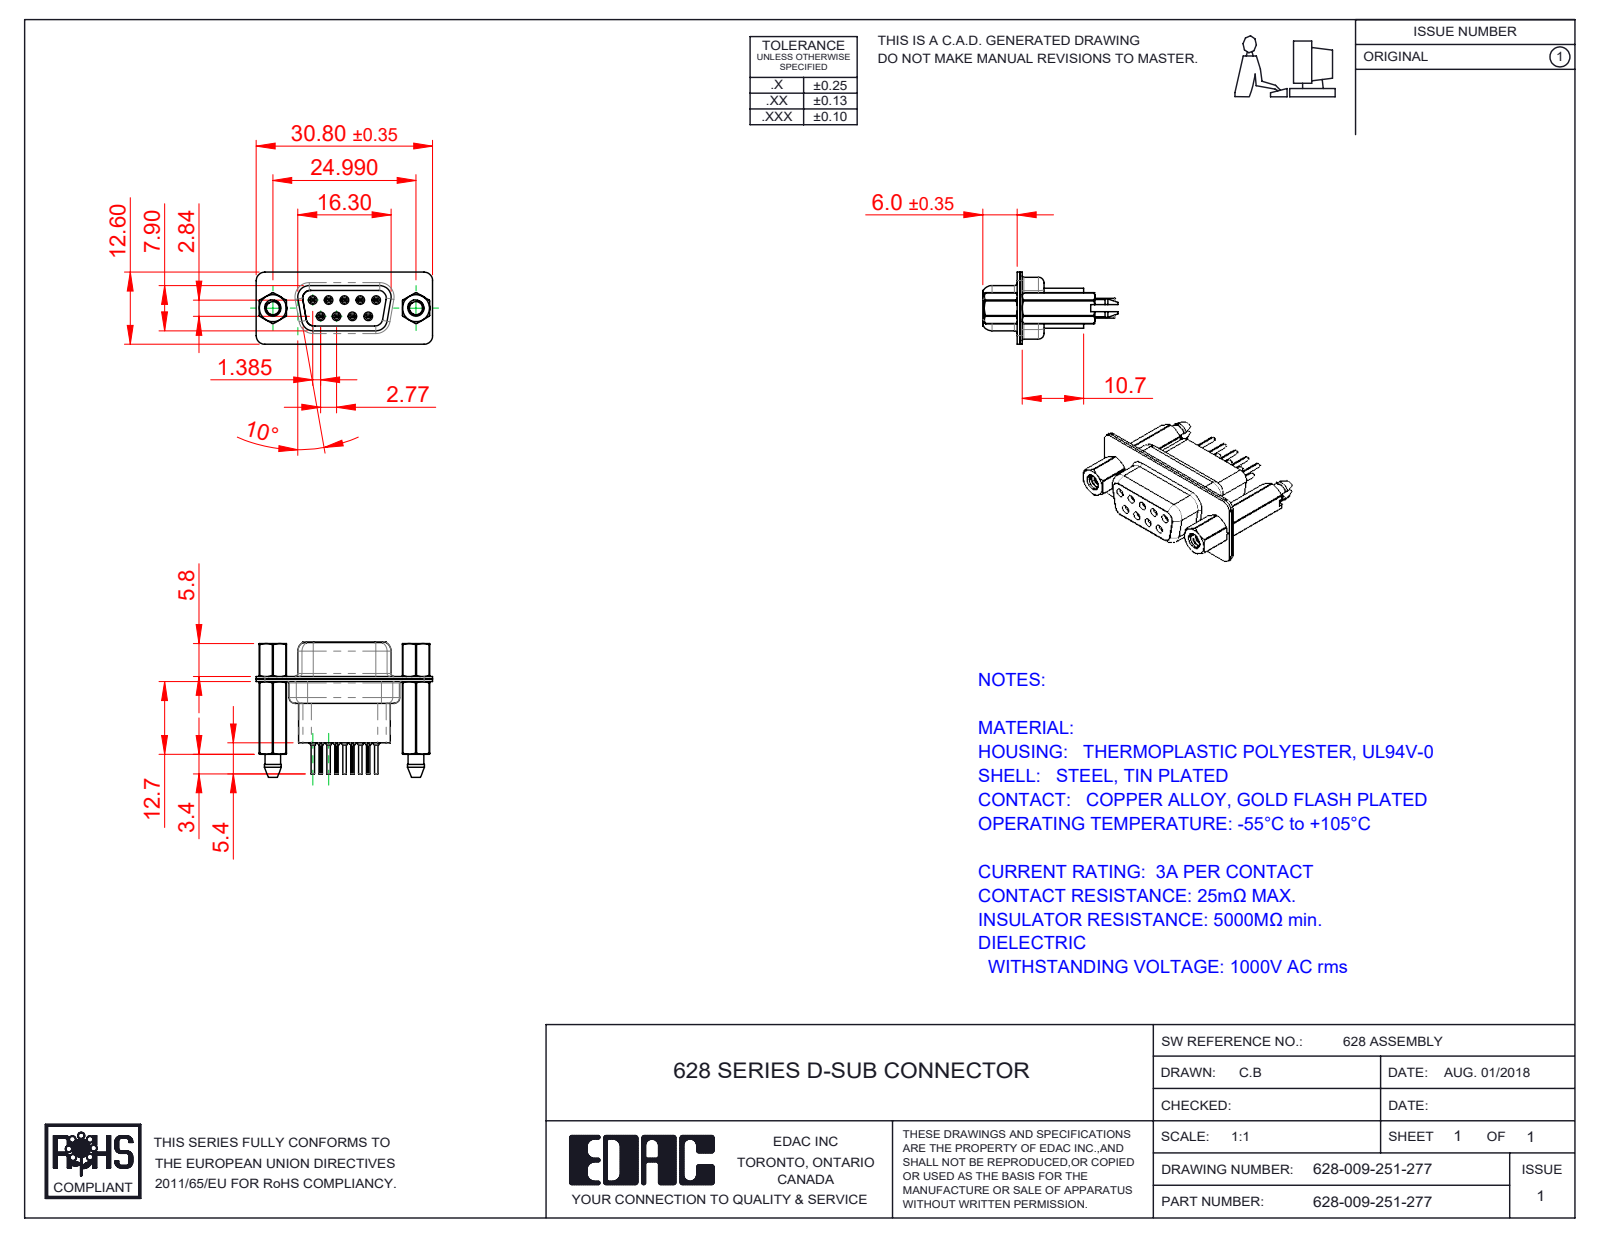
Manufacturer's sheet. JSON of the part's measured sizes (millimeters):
{"part_name": "628 Contact Row 2_51; 628 Shell Front_09 Contacts; 628 4-40 Hex Standoff; 628-009-251-277 (+4 more)", "step_written_by": "SolidWorks 2020 (CONFIG_CONTROL_DESIGN)", "units": "millimeters", "bodies": {"solids": 16, "faces": 1586, "planar": 400, "cylindrical": 538, "other": 648}, "overall_size": [30.8, 23.6, 12.6], "volume_mm3": 2771, "surface_area_mm2": 6452, "round_holes": [[0.2, 9], [0.8, 9], [0.9, 9], [1.1, 9], [1.6, 9], [1.7, 5], [2.26, 2], [2.29, 2], [4, 2], [4.05, 2], [4.85, 2]], "round_bosses_or_shafts": [[2, 9], [1.5, 9], [1.2, 9], [0.6, 9], [4.95, 2], [4.8, 2], [2.79, 2]], "partial_cylinders_radius": [[1.5, 19], [0.1, 18], [2, 12], [0.28, 9], [1.35, 6], [1.6, 6], [0.25, 4], [0.5, 4]], "face_to_face_distances": [0.45, 0.4, 0.9, 4.76, 8.5, 6.6, 1.9, 1.4, 7, 0.5], "hole_center_spacings": [3.16, 2.77, 5.54, 5.03, 5.04, 8.31, 7.48, 7.49]}
